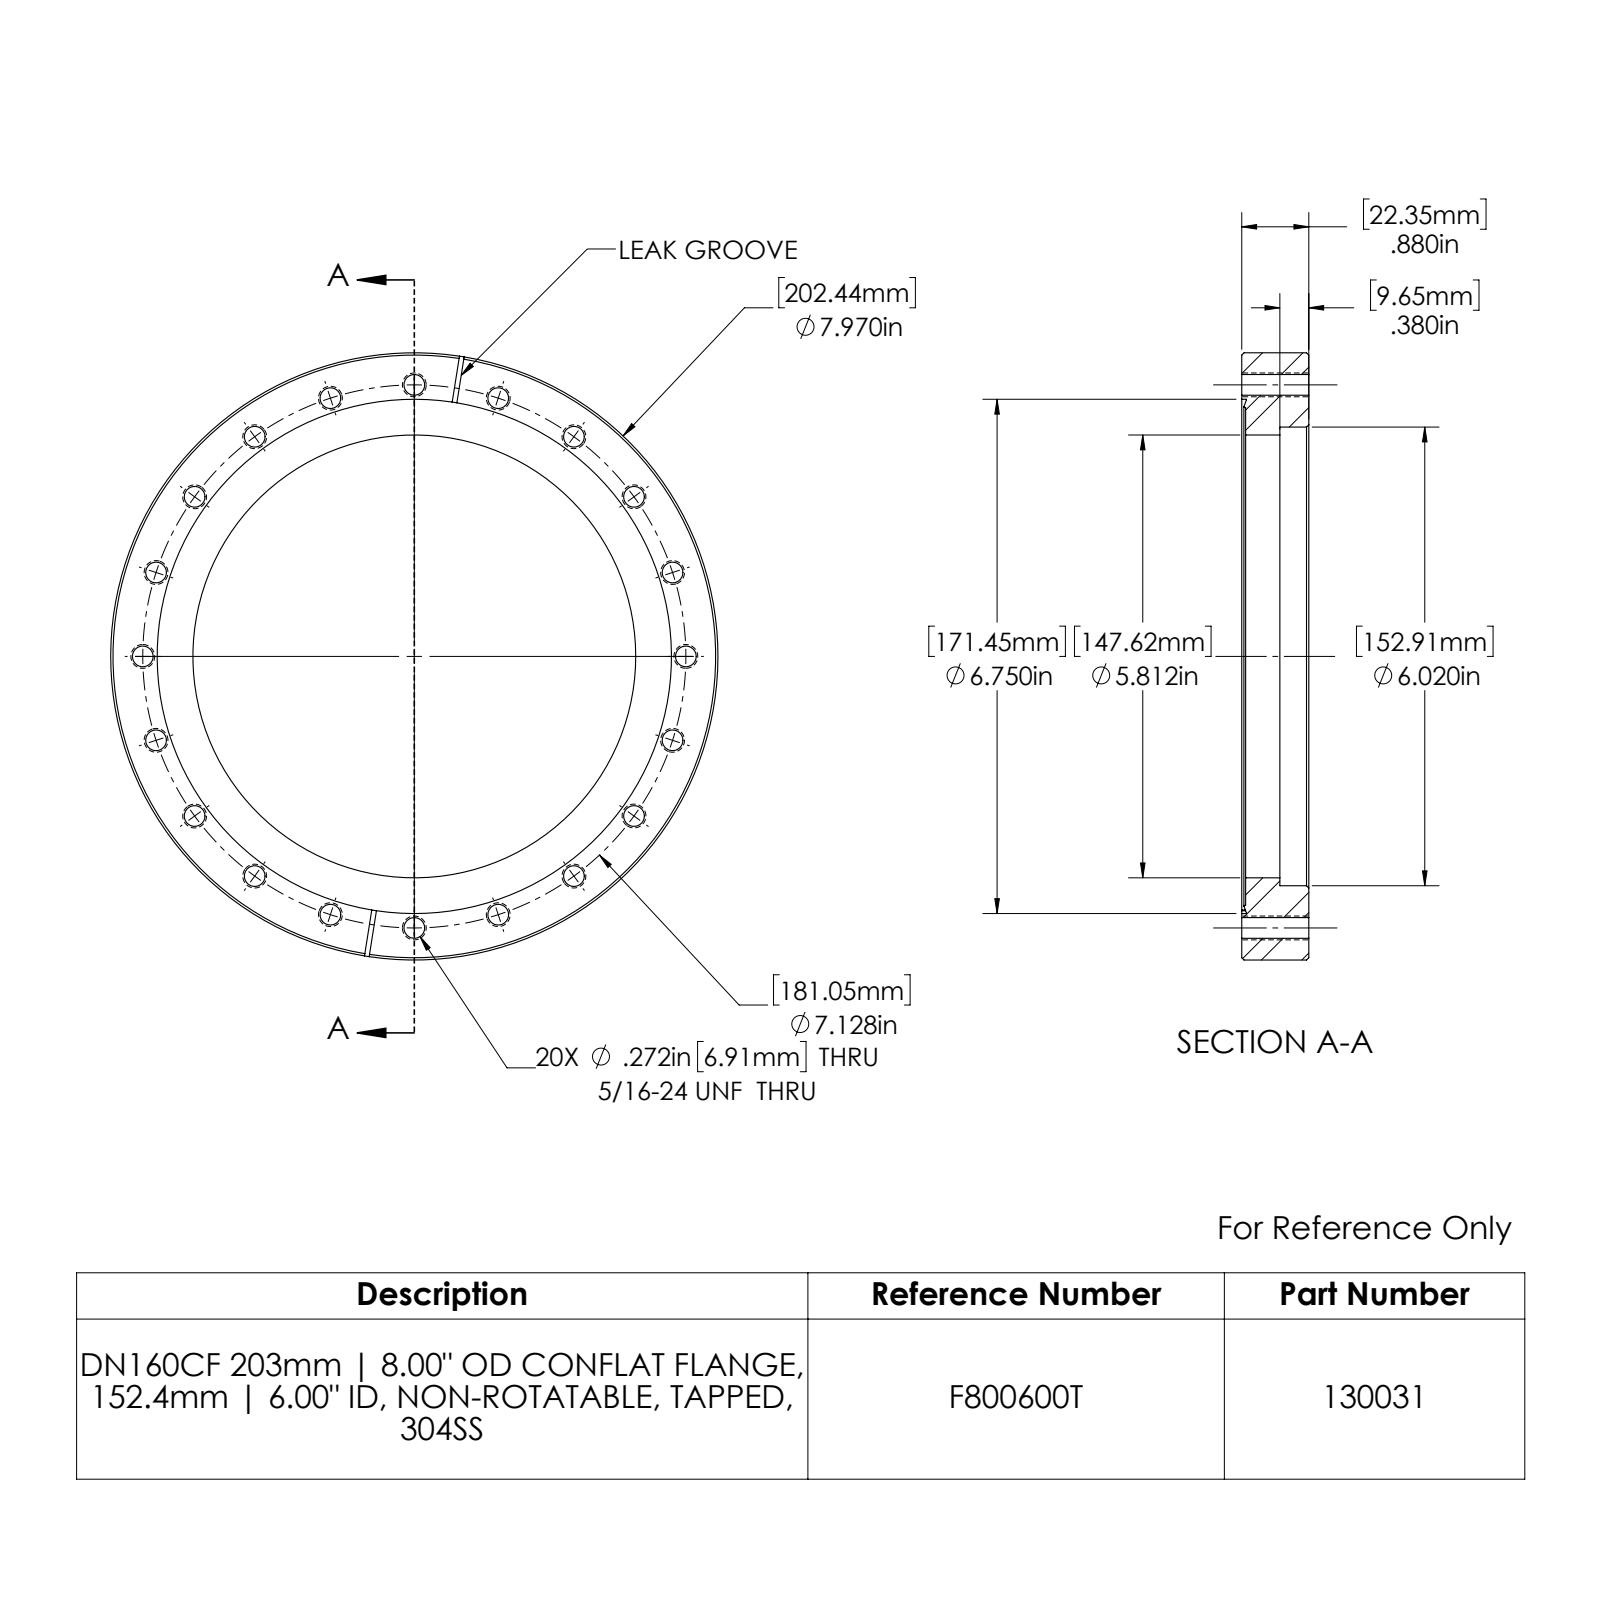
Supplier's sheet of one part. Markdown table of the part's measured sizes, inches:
| quantity | value |
| --- | --- |
| part name | 130031_D |
| STEP written by | SolidWorks 2022 (CONFIG_CONTROL_DESIGN) |
| units | inches |
| bodies | 1 solid, 78 faces (11 planar, 48 cylindrical, 19 other) |
| overall size | 7.97 × 7.97 × 0.88 |
| volume | 18.31 in³ |
| surface area | 97.45 in² |
| round holes (diameter × count) | 0.272 × 20, 5.812 × 1, 6.02 × 1, 6.75 × 1 |
| round bosses / shafts (diameter × count) | 7.97 × 1 |
| main face-to-face distances | 0.88, 0.051, 0.829, 0.5, 0.449, 0.38, 0.052, 0.448, 0.828, 0.062 |
| hole center spacings | 4.19, 1.115, 2.203, 5.767, 6.351, 7.04, 3.236, 3.564 |
